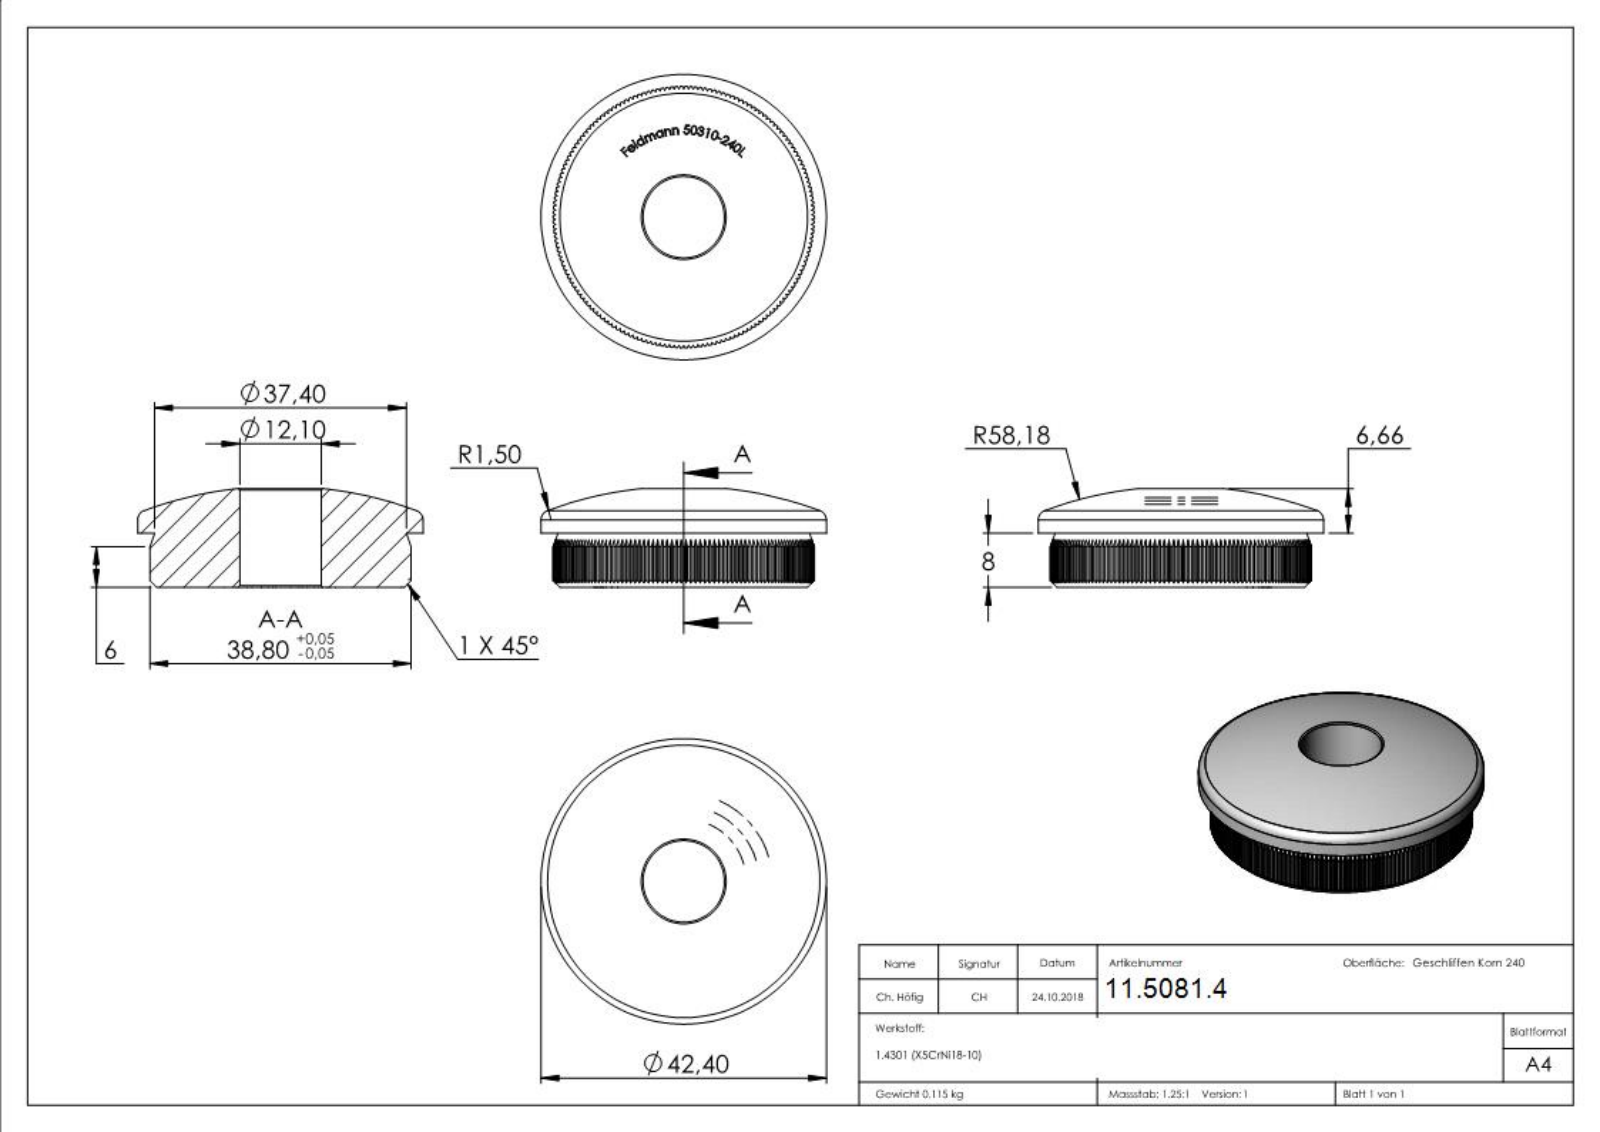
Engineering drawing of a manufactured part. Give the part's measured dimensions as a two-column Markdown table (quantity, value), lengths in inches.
| quantity | value |
| --- | --- |
| part name | 50310-240L |
| STEP written by | SolidWorks 2015 (CONFIG_CONTROL_DESIGN) |
| units | inches |
| bodies | 1 solid, 783 faces (489 planar, 174 cylindrical, 120 other) |
| overall size | 1.669 × 1.669 × 0.577 |
| volume | 0.891 in³ |
| surface area | 7.663 in² |
| round holes (diameter × count) | 0.476 × 1 |
| round bosses / shafts (diameter × count) | 1.669 × 1 |
| partial cylindrical surfaces (radius × count) | 0.764 × 1 |
| main face-to-face distances | 0.315, 0.75, 0.75, 0.751, 0.311, 0.749, 0.021, 0.026, 0.033, 0.028 |
